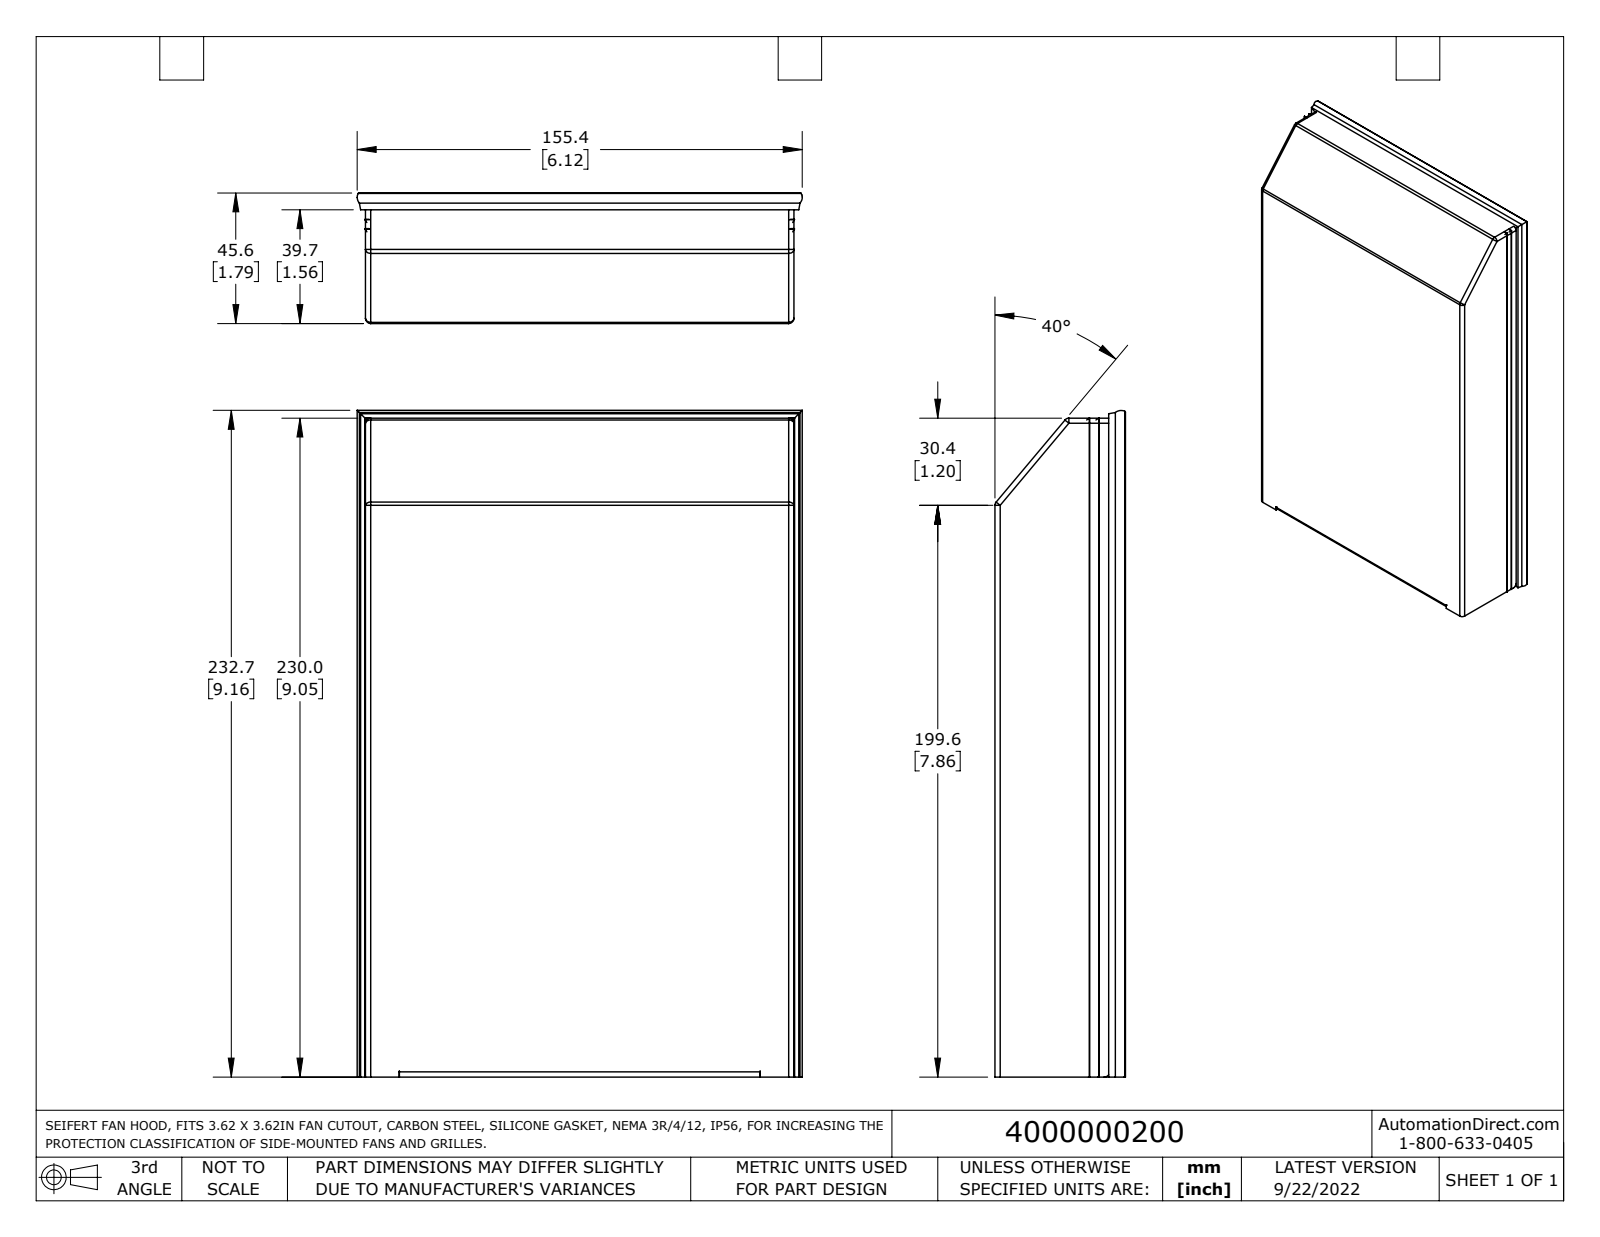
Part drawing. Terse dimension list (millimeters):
name: fc4000_000
written by: SolidWorks 2021 (AUTOMOTIVE_DESIGN)
unit: mm
bodies: 11 solids, 443 faces (199 planar, 206 cylindrical, 38 other)
size: 232.7 × 155.4 × 45.6
volume: 128 000 mm³; area: 228 200 mm²
holes: 4× ⌀5.5, 2× ⌀3.4, 2× ⌀5, 2× ⌀6
rounds: 23× R3, 15× R1.8, 12× R0.1, 12× R7.1, 12× R30, 11× R1, 9× R0.2, 9× R0.8
face distances: 0.8, 148, 1.5, 148.8, 5.8, 5, 140, 1.6, 143, 9.6
hole spacings: 80, 164, 182.5, 120
